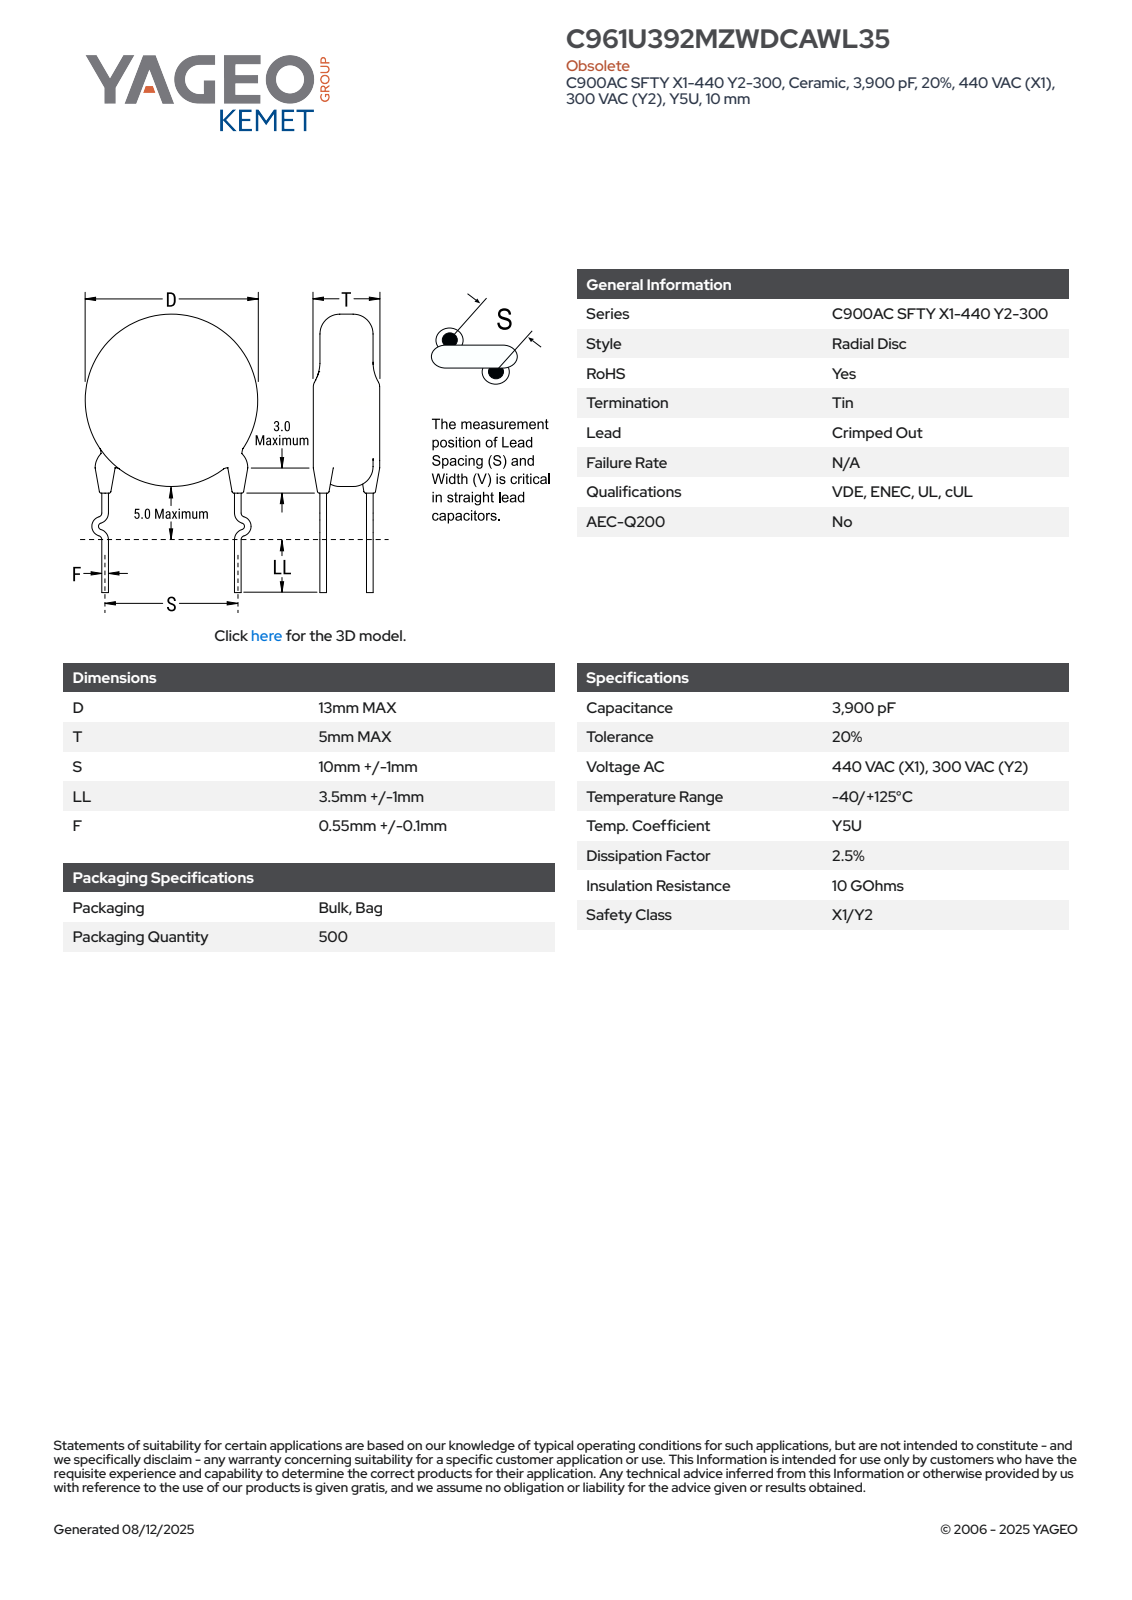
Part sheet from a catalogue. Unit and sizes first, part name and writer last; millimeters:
Units: millimetres
Overall size (bounding box): 22.5 × 15.07 × 5
Round bosses / shafts (diameter × count): ⌀1.2 ×2, ⌀13 ×1
Main face-to-face distances: 5, 7.19, 5.84, 1.35, 0.37, 0.33, 1.09, 5.52, 2.79, 4.01
Volume: 660 mm³ · Surface area: 510 mm²
Bodies: 4 solids, 85 faces (63 planar, 6 cylindrical, 16 other)
Part name (STEP PRODUCT): CCD_KCOC900_D13T5S10LL4.5F0.55
STEP written by: SolidWorks 2014 (AUTOMOTIVE_DESIGN)
